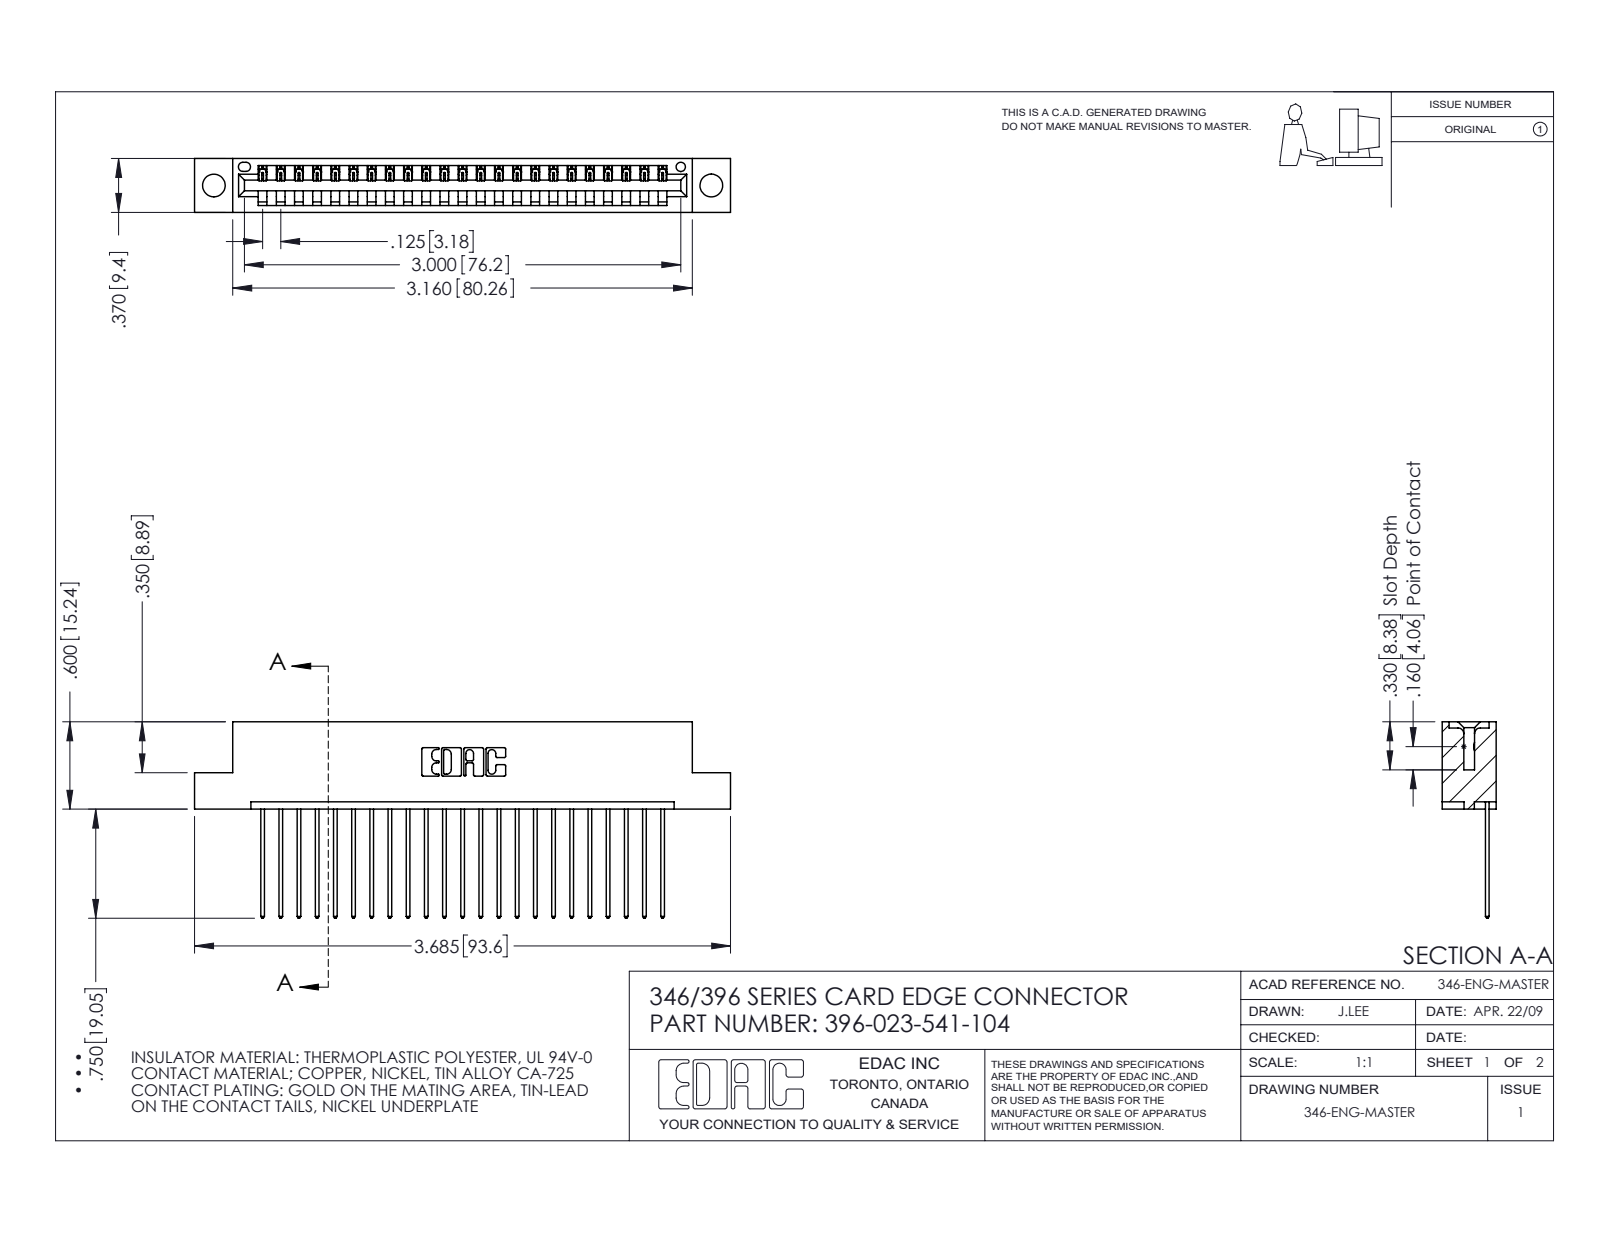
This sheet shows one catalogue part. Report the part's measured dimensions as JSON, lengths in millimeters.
{"part_name": "396-023-541-104; 346 Part_Flush Mounting Lugs - 0.156 Dia-TH; 345-292-001_345-293-141", "step_written_by": "SolidWorks 2016 (CONFIG_CONTROL_DESIGN)", "units": "millimeters", "bodies": {"solids": 24, "faces": 1456, "planar": 996, "cylindrical": 460, "other": 0}, "overall_size": [93.6, 34.3, 9.4], "volume_mm3": 8820, "surface_area_mm2": 11070, "round_holes": [[4, 2], [1.6, 1]], "partial_cylinders_radius": [[0.2, 46], [0.3, 46], [0.3, 22], [0.2, 6], [0.8, 6], [0.7, 3], [0.8, 2], [1, 2]], "face_to_face_distances": [1.2, 8.2, 6.4, 9.4, 1.8, 7.6, 0.6, 3.8, 5.6, 2.5], "hole_center_spacings": [6.2, 81.6, 86.9]}
